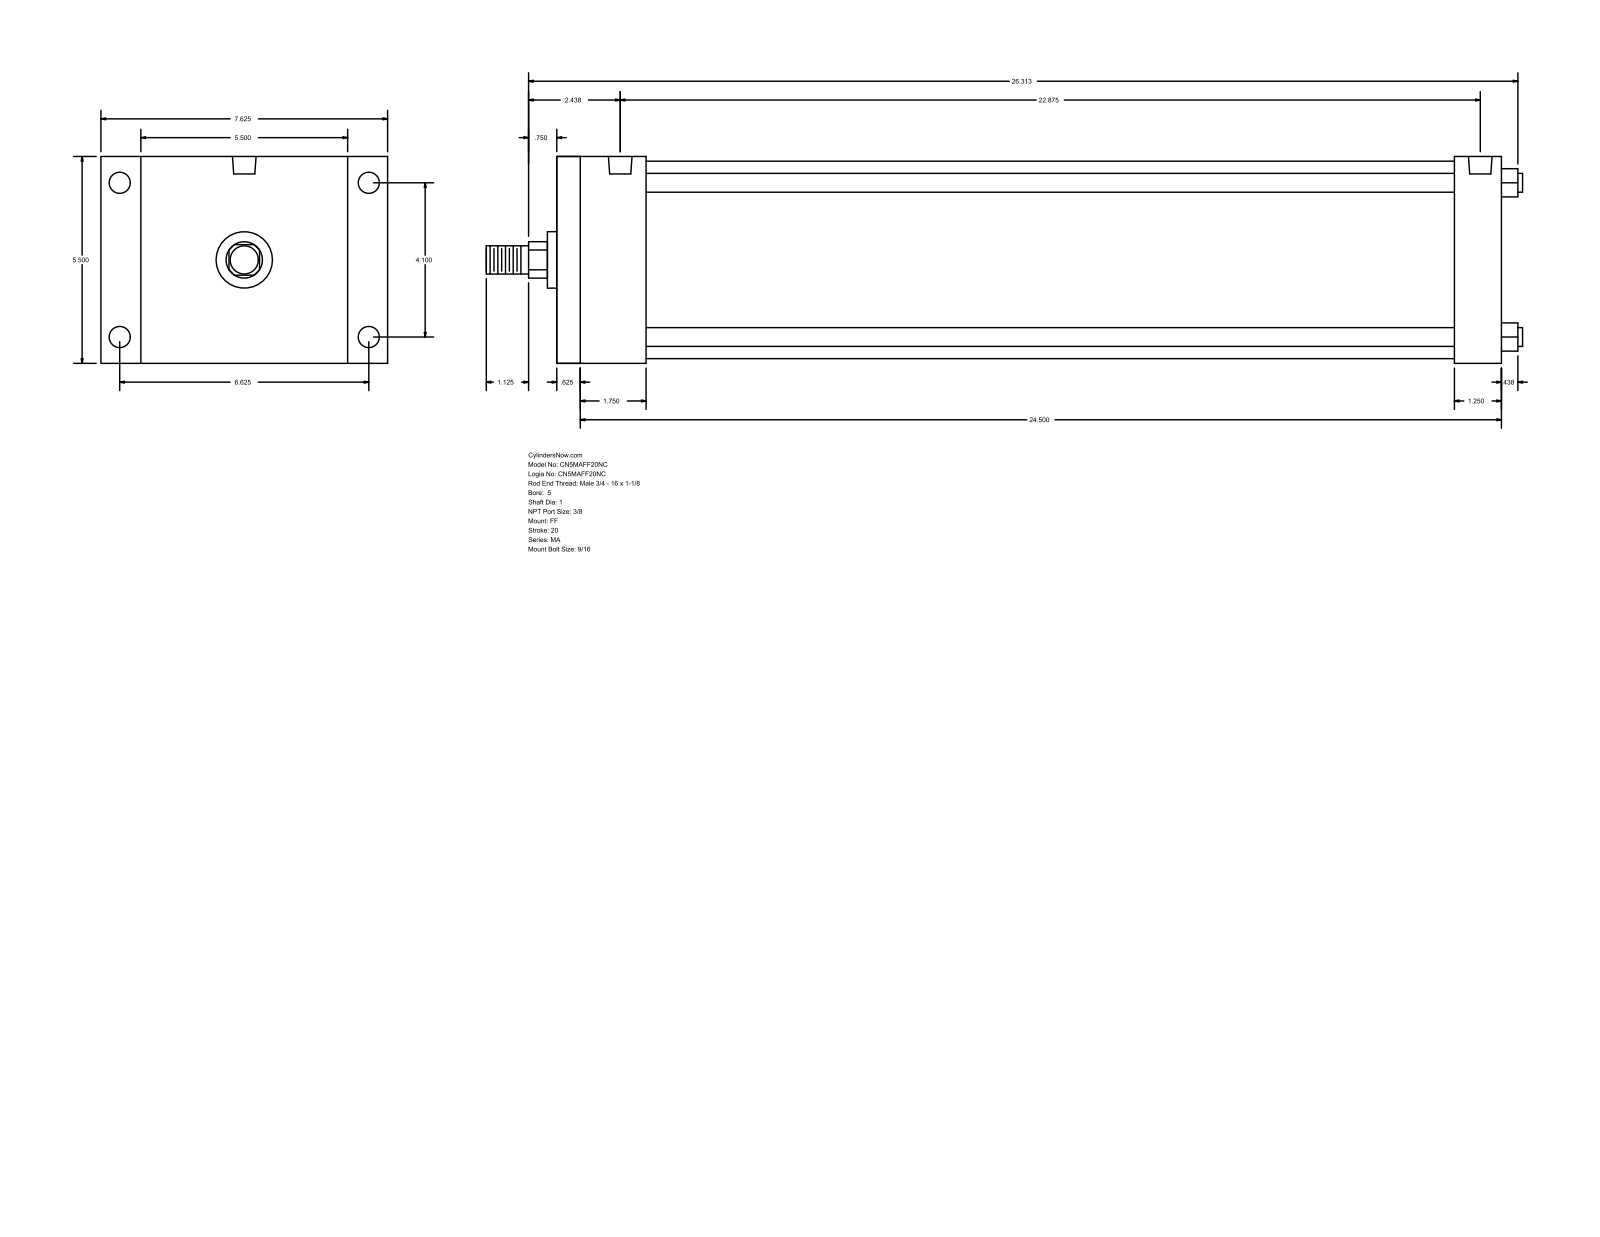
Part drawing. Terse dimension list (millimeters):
name: MA_FF__0500_1
written by: GSSL Pune (CONFIG_CONTROL_DESIGN)
unit: mm
bodies: 0 solids, 92 faces (64 planar, 28 cylindrical, 0 other)
size: 700.09 × 193.68 × 139.7
holes: 4× ⌀11.11, 4× ⌀14.29, 2× ⌀15.93
bosses: 4× ⌀12.7, 1× ⌀133.35, 1× ⌀38.1, 1× ⌀25.4, 1× ⌀19.05
rounds: 1× R12.29
face distances: 139.7, 638.18, 15.87, 622.31, 606.43, 590.56, 31.75, 60.33, 44.46, 546.1
hole spacings: 104.14, 168.28, 197.9, 571.5, 4.76, 4.77, 576.26, 576.27
